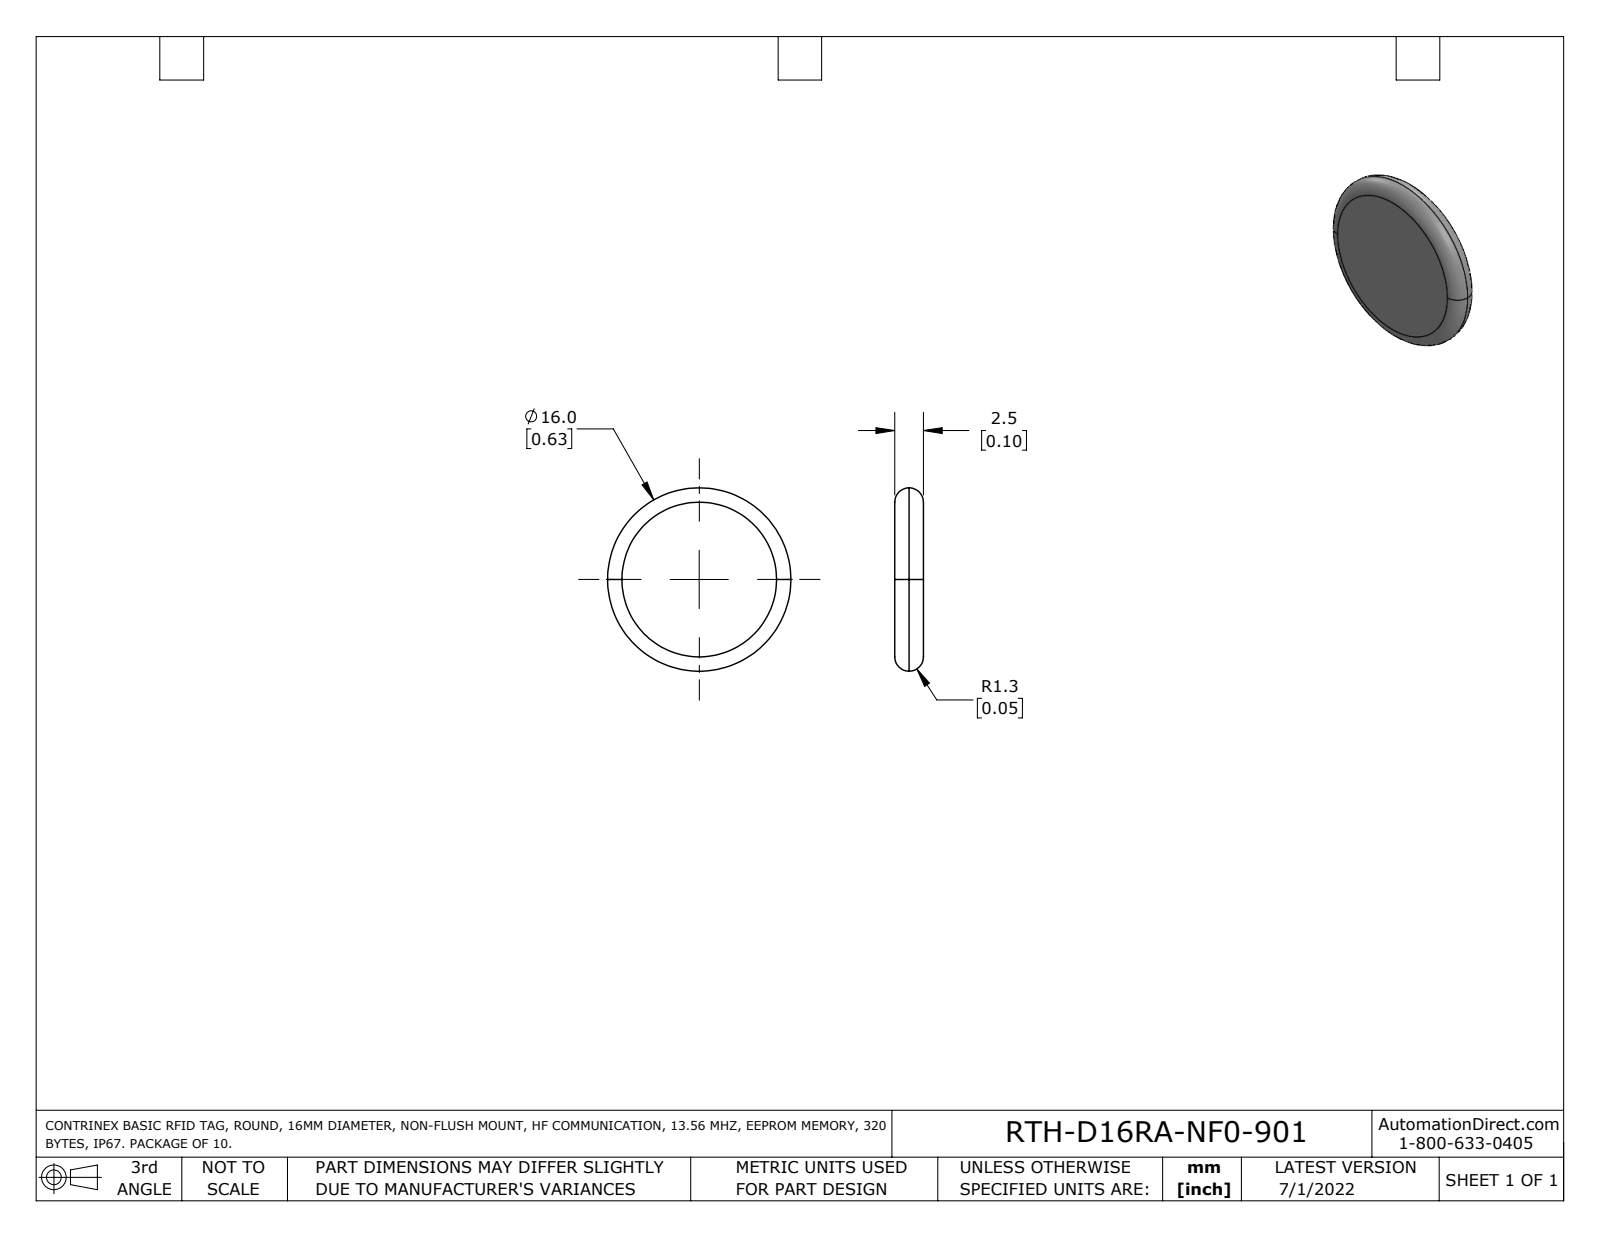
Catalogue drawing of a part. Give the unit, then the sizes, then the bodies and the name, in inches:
Units: inches
Overall size (bounding box): 0.63 × 0.63 × 0.098
Main face-to-face distances: 0.098
Volume: 0.029 in³ · Surface area: 0.732 in²
Bodies: 1 solid, 6 faces (2 planar, 0 cylindrical, 4 other)
Part name (STEP PRODUCT): RTP-0160-020
STEP written by: SolidWorks 2021 (AUTOMOTIVE_DESIGN)
